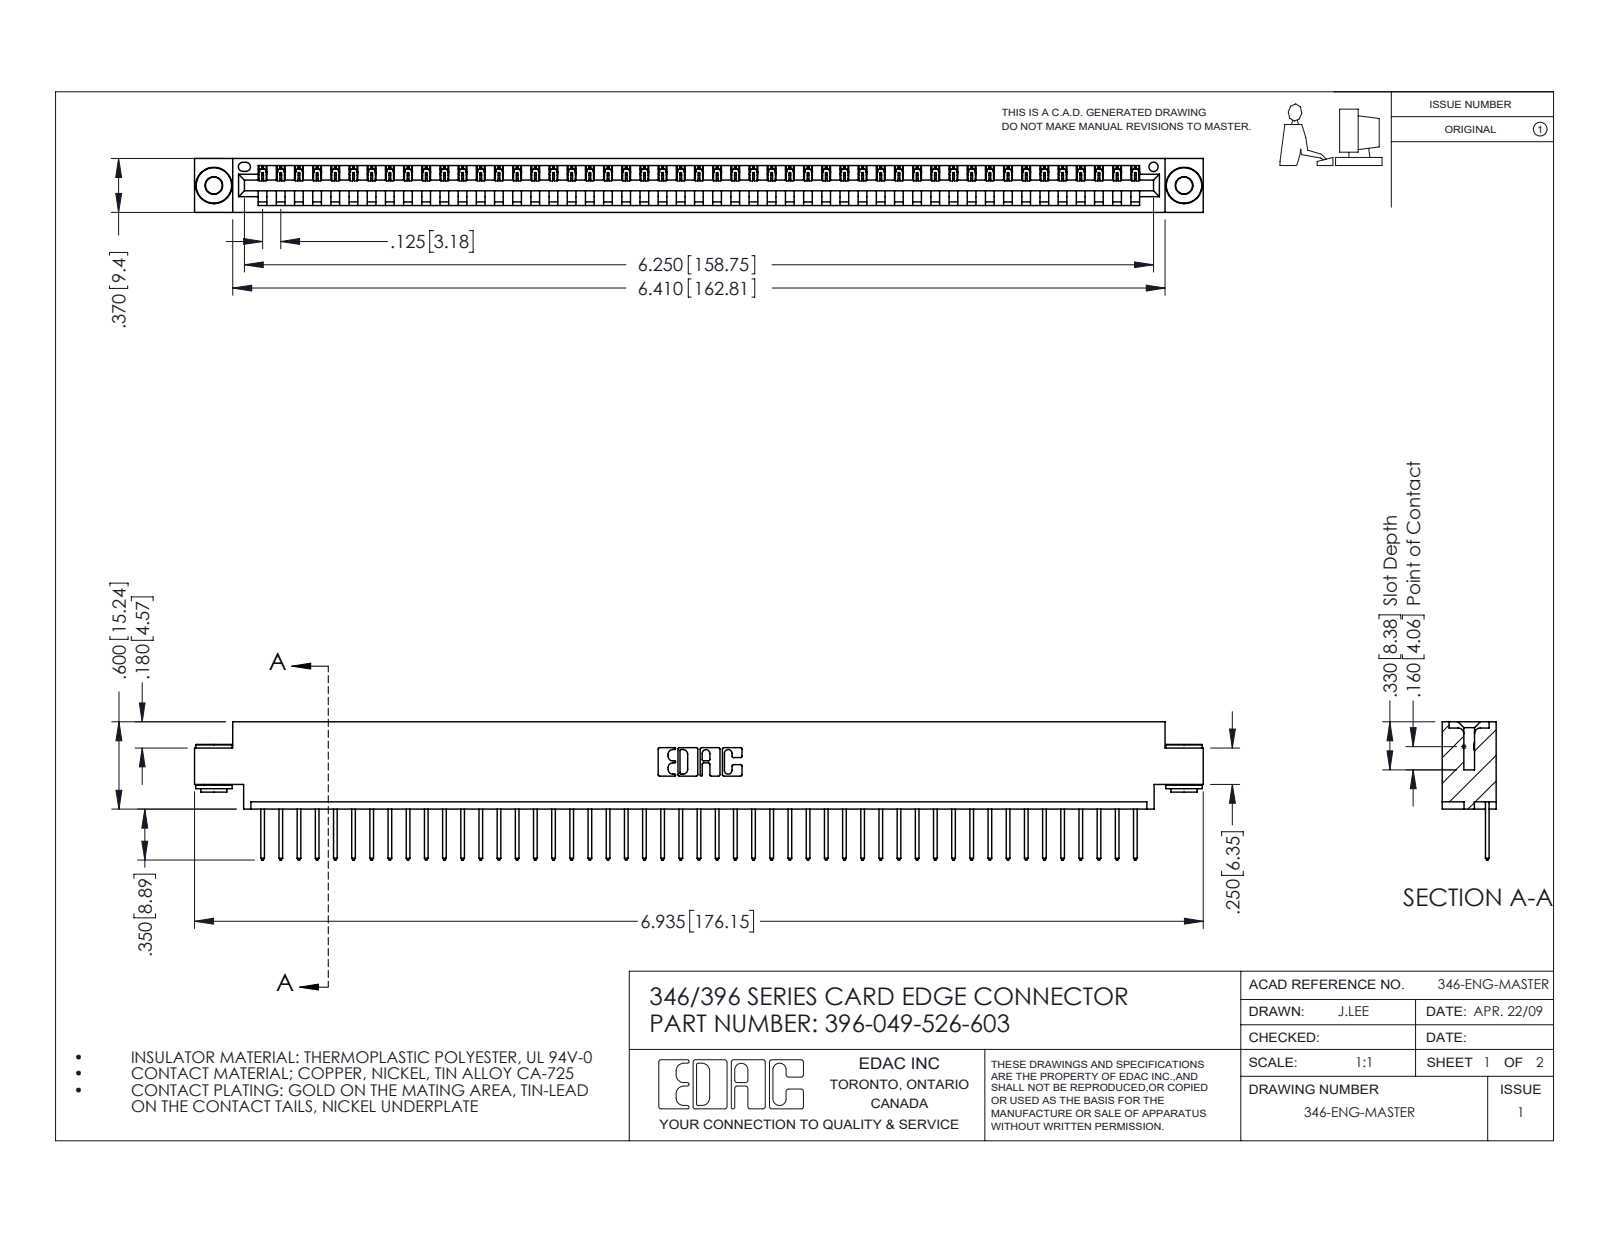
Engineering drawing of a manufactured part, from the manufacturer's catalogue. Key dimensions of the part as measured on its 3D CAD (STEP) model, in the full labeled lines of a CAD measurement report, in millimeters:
Part name (STEP PRODUCT): 345-250-002_345-250-002-102; 345-292-001_345-293-126; 346 Part_0.170 Offset - 0.156 Dia-TH; 396-049-526-603
STEP written by: SolidWorks 2016 (CONFIG_CONTROL_DESIGN)
Units: millimetres
Bodies: 52 solids, 3006 faces (2050 planar, 948 cylindrical, 8 other)
Overall size (bounding box): 176.1 × 24.1 × 9.4
Volume: 16 730 mm³ · Surface area: 21 320 mm²
Round holes (diameter × count): ⌀2.9 ×2, ⌀4 ×2, ⌀1.6 ×1
Round bosses / shafts (diameter × count): ⌀6.4 ×2, ⌀4.6 ×2, ⌀3.5 ×2
Partial cylindrical surfaces — rounded edges, fillets, slot ends (radius × count): R0.2 ×98, R0.3 ×98, R0.3 ×22, R0.2 ×6, R0.8 ×6, R0.7 ×3, R0.8 ×2, R1 ×2
Main face-to-face distances: 1.2, 8.2, 9.4, 6.4, 0.6, 1.8, 7.6, 3.8, 5.6, 2.5
Hole centre spacings: 6.2, 164.1, 169.4
